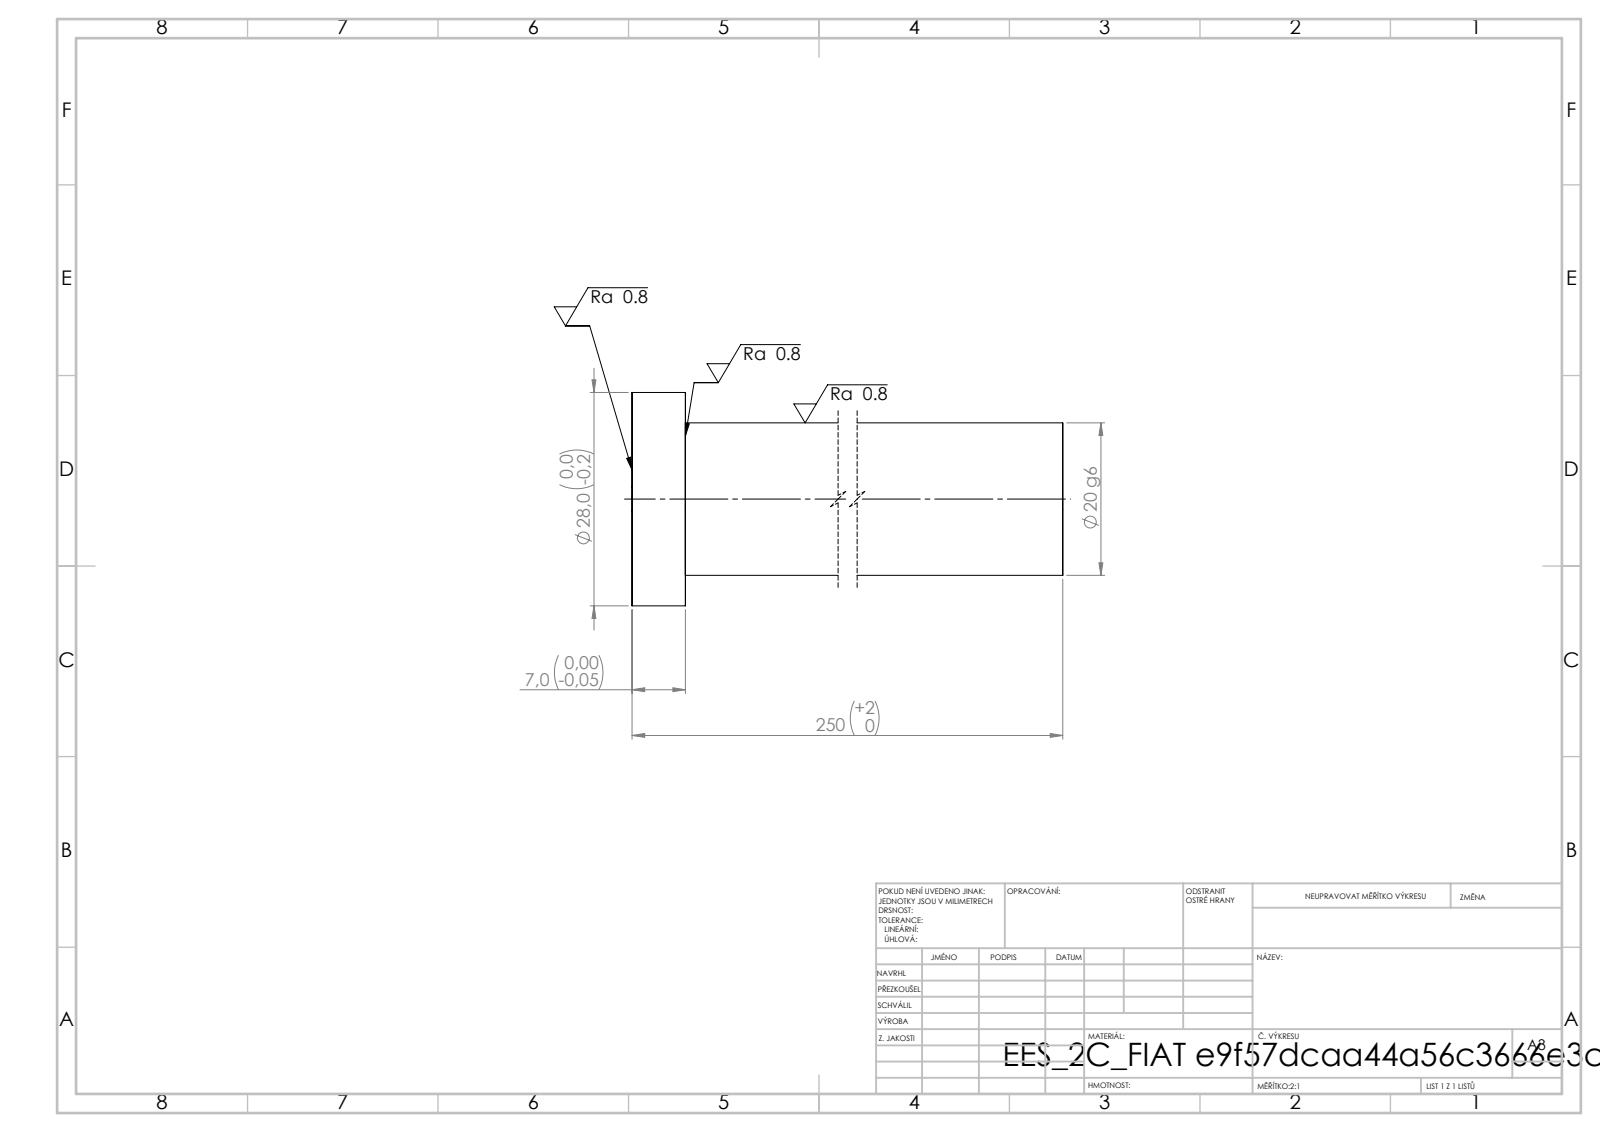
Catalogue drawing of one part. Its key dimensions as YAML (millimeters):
step_written_by: "SolidWorks 2019 (CONFIG_CONTROL_DESIGN)"
units: millimeters
bodies: {solids: 1, faces: 7, planar: 3, cylindrical: 4, other: 0}
overall_size: [250, 28, 28]
volume: 80651
surface_area: 17115
round_bosses_or_shafts:
  - {diameter: 28, count: 1}
  - {diameter: 20, count: 1}
face_to_face_distances: [250, 7, 243]
